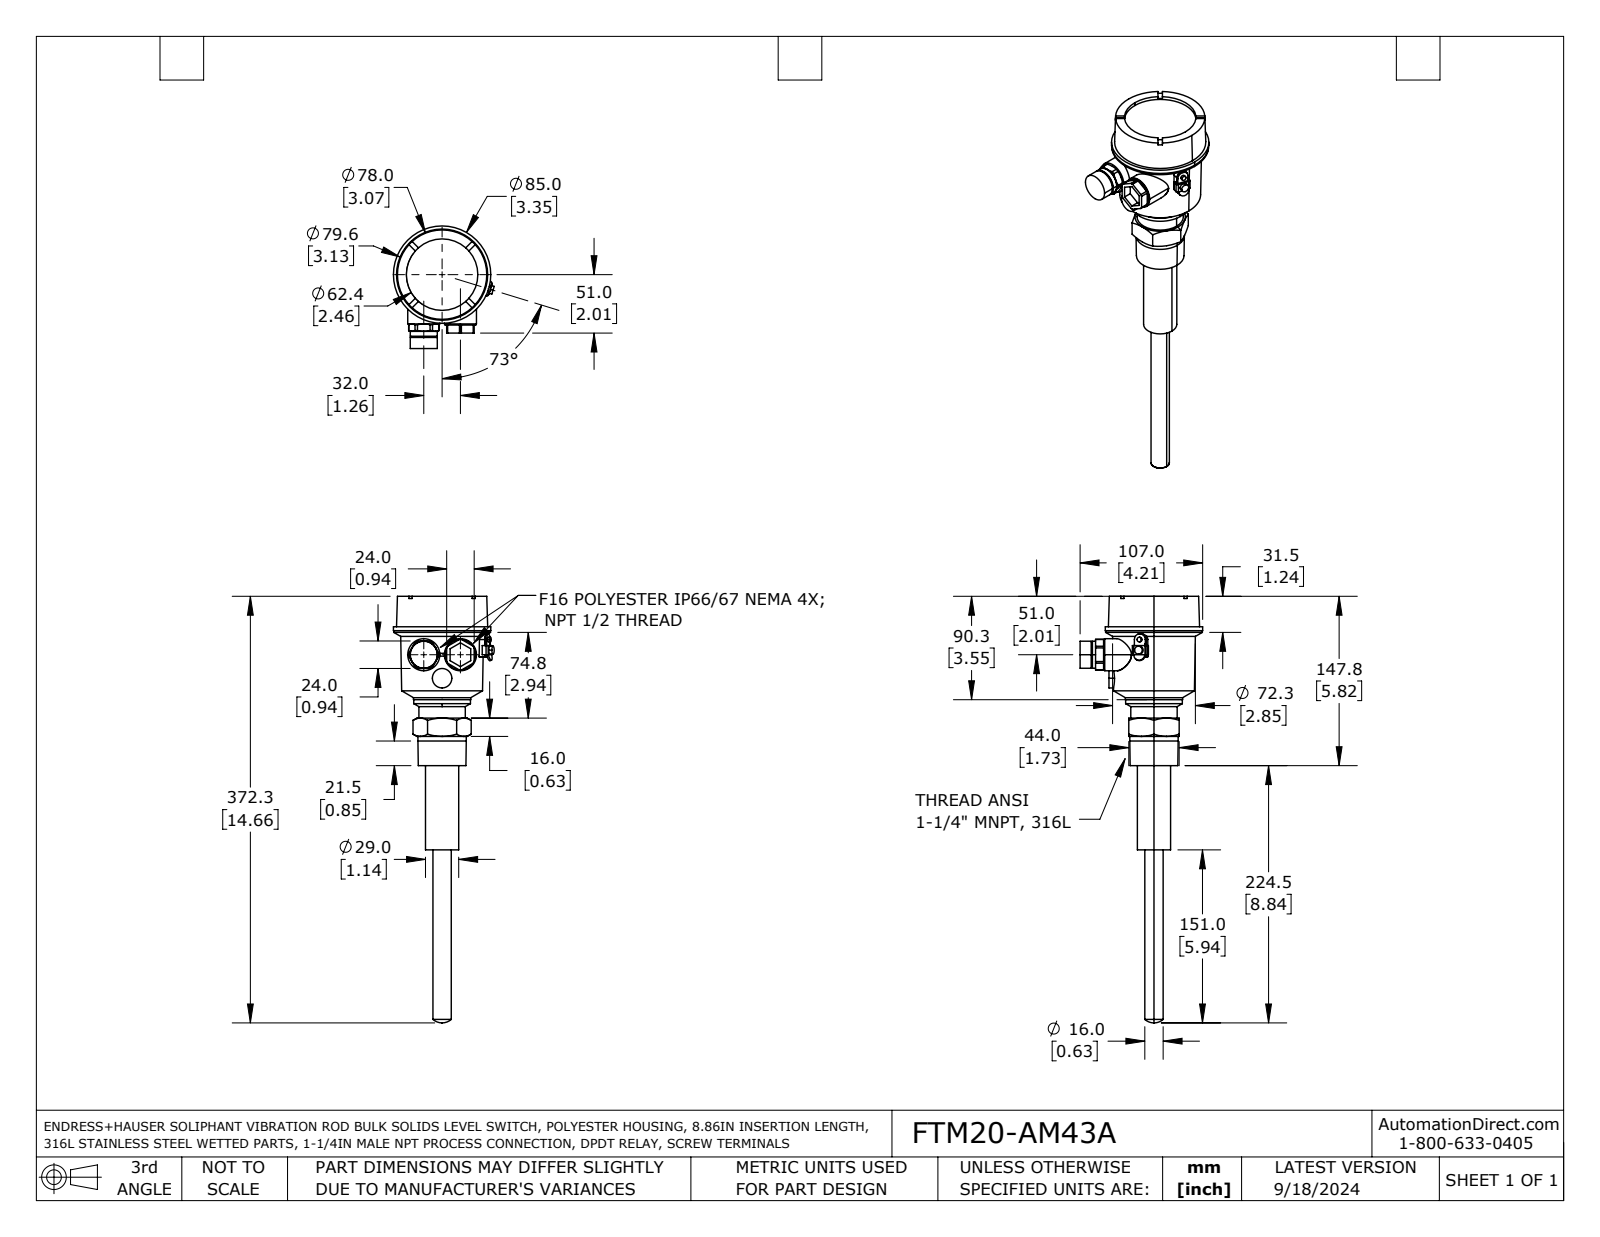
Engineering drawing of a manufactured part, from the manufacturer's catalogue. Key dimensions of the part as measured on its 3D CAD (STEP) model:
Part name (STEP PRODUCT): FTM20-AM43A
STEP written by: SolidWorks 2021 (AUTOMOTIVE_DESIGN)
Units: inches
Bodies: 1 solid, 222 faces (112 planar, 56 cylindrical, 54 other)
Overall size (bounding box): 14.657 × 4.213 × 3.464
Volume: 34.74 in³ · Surface area: 92.31 in²
Round holes (diameter × count): ⌀2.457 ×1
Round bosses / shafts (diameter × count): ⌀1.102 ×2, ⌀3.346 ×1, ⌀3.327 ×1, ⌀1.969 ×1, ⌀1.949 ×1, ⌀1.661 ×1, ⌀1.594 ×1, ⌀1.142 ×1
Partial cylindrical surfaces — rounded edges, fillets, slot ends (radius × count): R0.059 ×3, R0.197 ×1, R0.52 ×1
Main face-to-face distances: 0.118, 1.732, 0.929, 1.047, 4.772, 5.701, 5.819, 0.827, 2.894, 7.665
